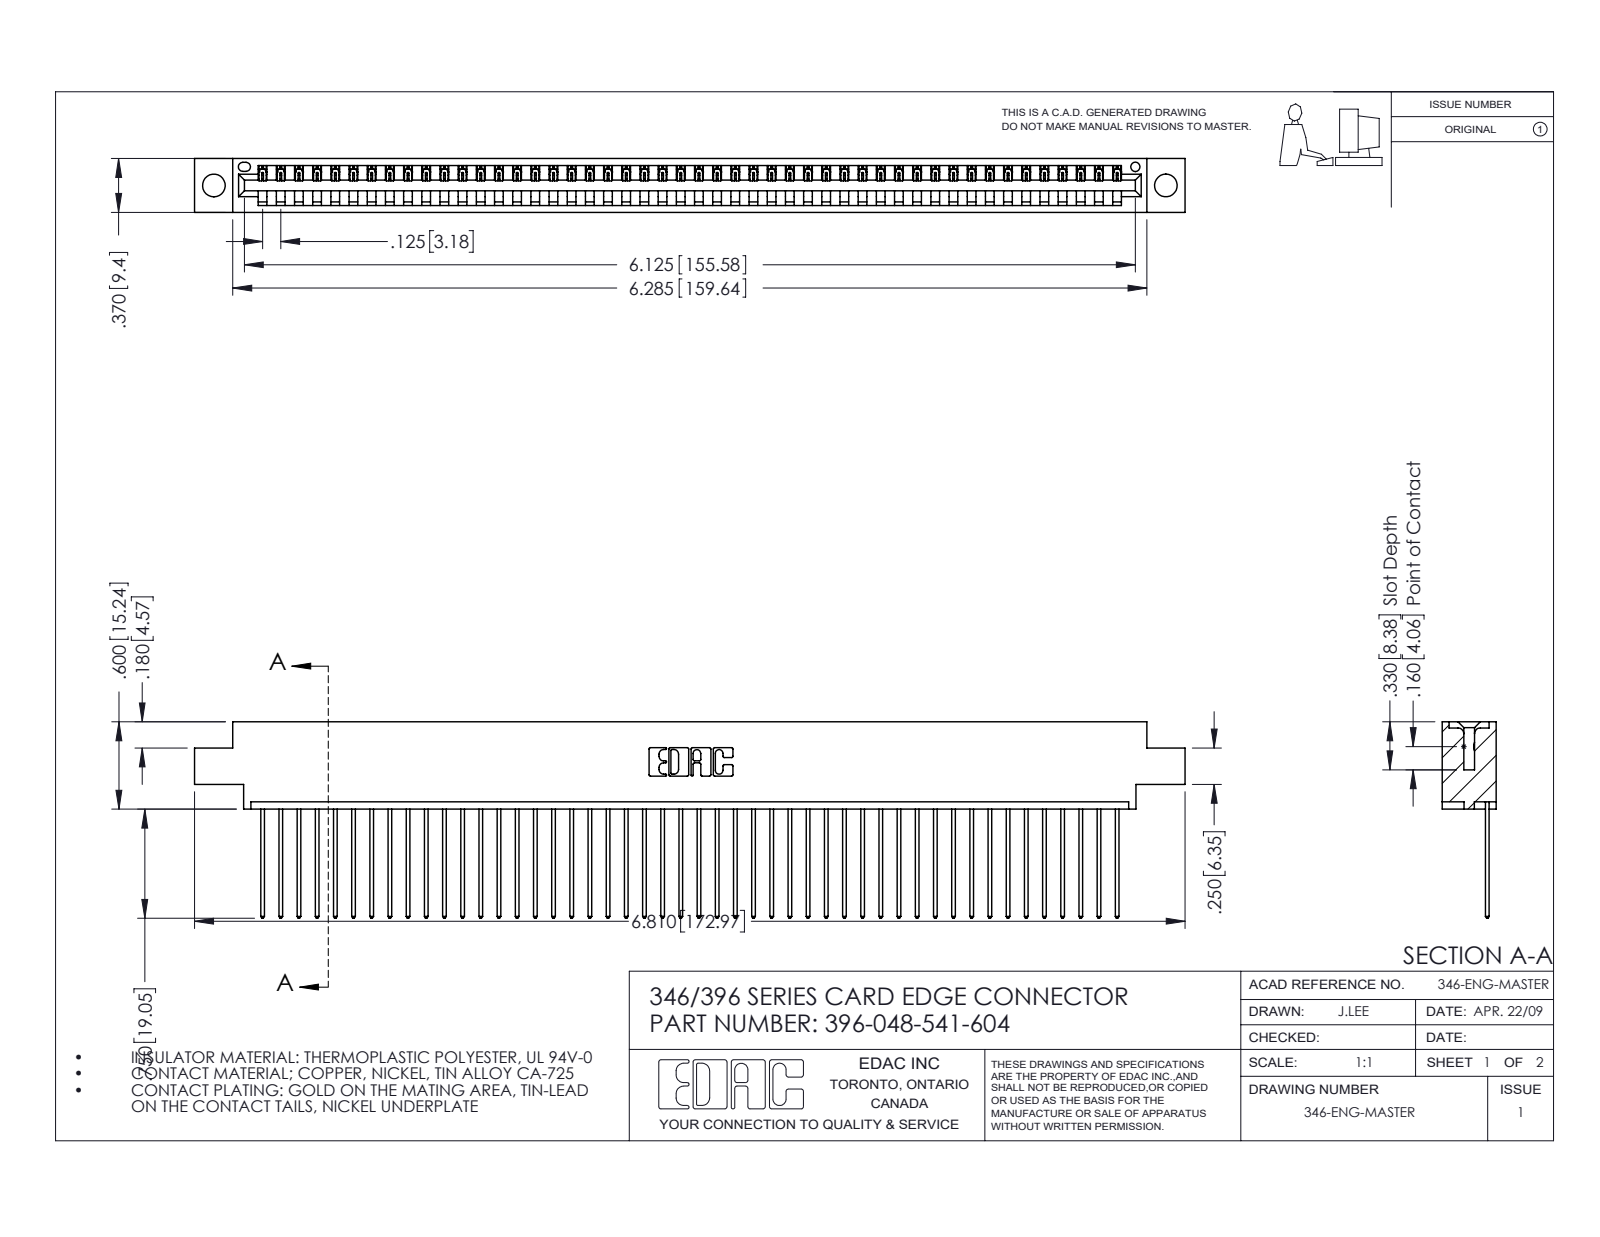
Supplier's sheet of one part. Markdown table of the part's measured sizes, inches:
| quantity | value |
| --- | --- |
| part name | 345-292-001_345-293-141; 396-048-541-604; 346 Part_0.170 Offset - 0.156 Dia-TH |
| STEP written by | SolidWorks 2016 (CONFIG_CONTROL_DESIGN) |
| units | inches |
| bodies | 49 solids, 2910 faces (2000 planar, 910 cylindrical, 0 other) |
| overall size | 6.81 × 1.35 × 0.37 |
| volume | 1.008 in³ |
| surface area | 33.51 in² |
| round holes (diameter × count) | 0.156 × 2, 0.064 × 1 |
| partial cylindrical surfaces (radius × count) | 0.006 × 96, 0.01 × 96, 0.01 × 22, 0.007 × 6, 0.031 × 6, 0.026 × 3, 0.031 × 2, 0.04 × 2 |
| main face-to-face distances | 0.048, 0.322, 0.37, 0.25, 0.072, 0.298, 0.025, 0.148, 0.222, 0.1 |
| hole center spacings | 0.246, 6.336, 6.545 |
